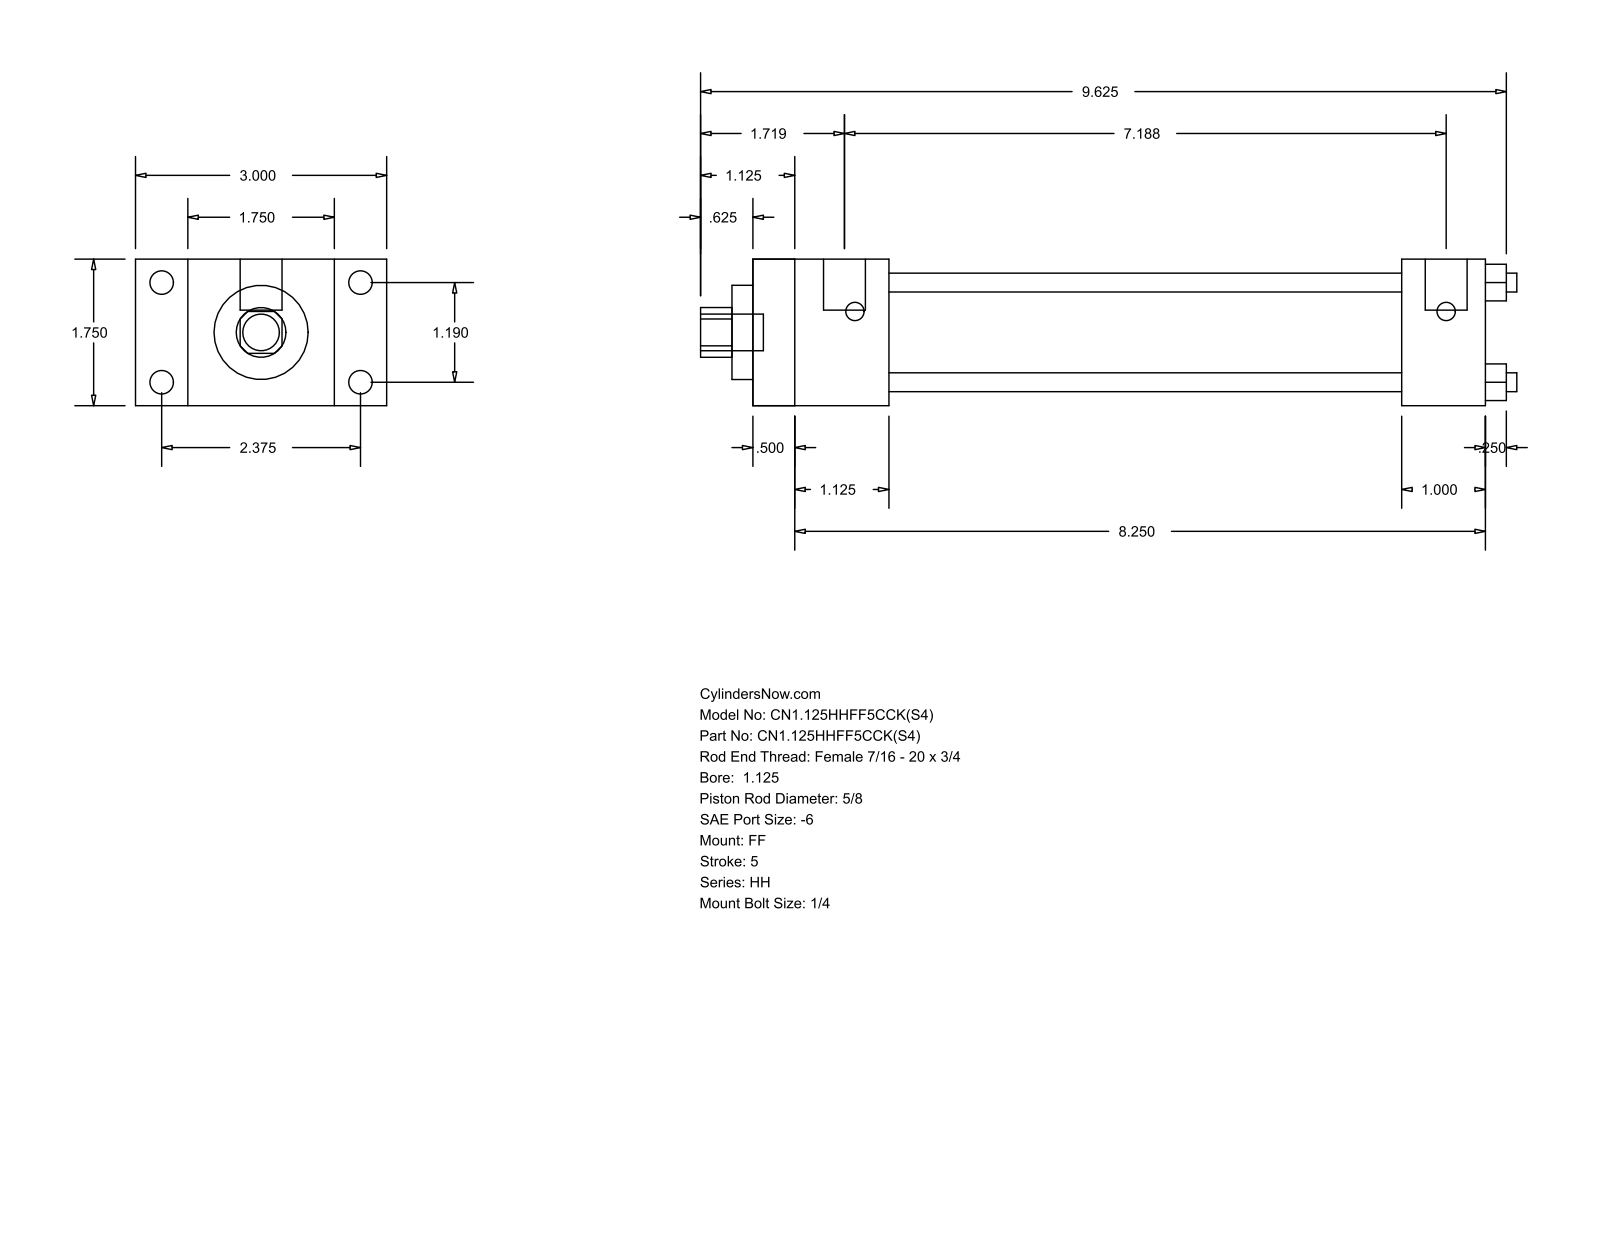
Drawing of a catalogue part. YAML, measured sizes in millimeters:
part_name: "HH_FF__0112_0.625"
step_written_by: "GSSL Pune (CONFIG_CONTROL_DESIGN)"
units: millimeters
bodies: {solids: 0, faces: 92, planar: 64, cylindrical: 28, other: 0}
overall_size: [247.65, 76.2, 44.45]
round_holes:
  - {diameter: 5.71, count: 4}
  - {diameter: 15.88, count: 1}
  - {diameter: 28.57, count: 1}
  - {diameter: 34.92, count: 1}
round_bosses_or_shafts:
  - {diameter: 7.14, count: 4}
  - {diameter: 5.56, count: 4}
  - {diameter: 12.7, count: 2}
  - {diameter: 11.11, count: 1}
partial_cylinders:
  - {radius: 7.54, count: 1}
face_to_face_distances: [44.46, 222.24, 12.69, 209.55, 15.87, 60.33, 28.58, 41.27, 196.84, 184.15]
hole_center_spacings: [21.37, 30.22, 42.74]
